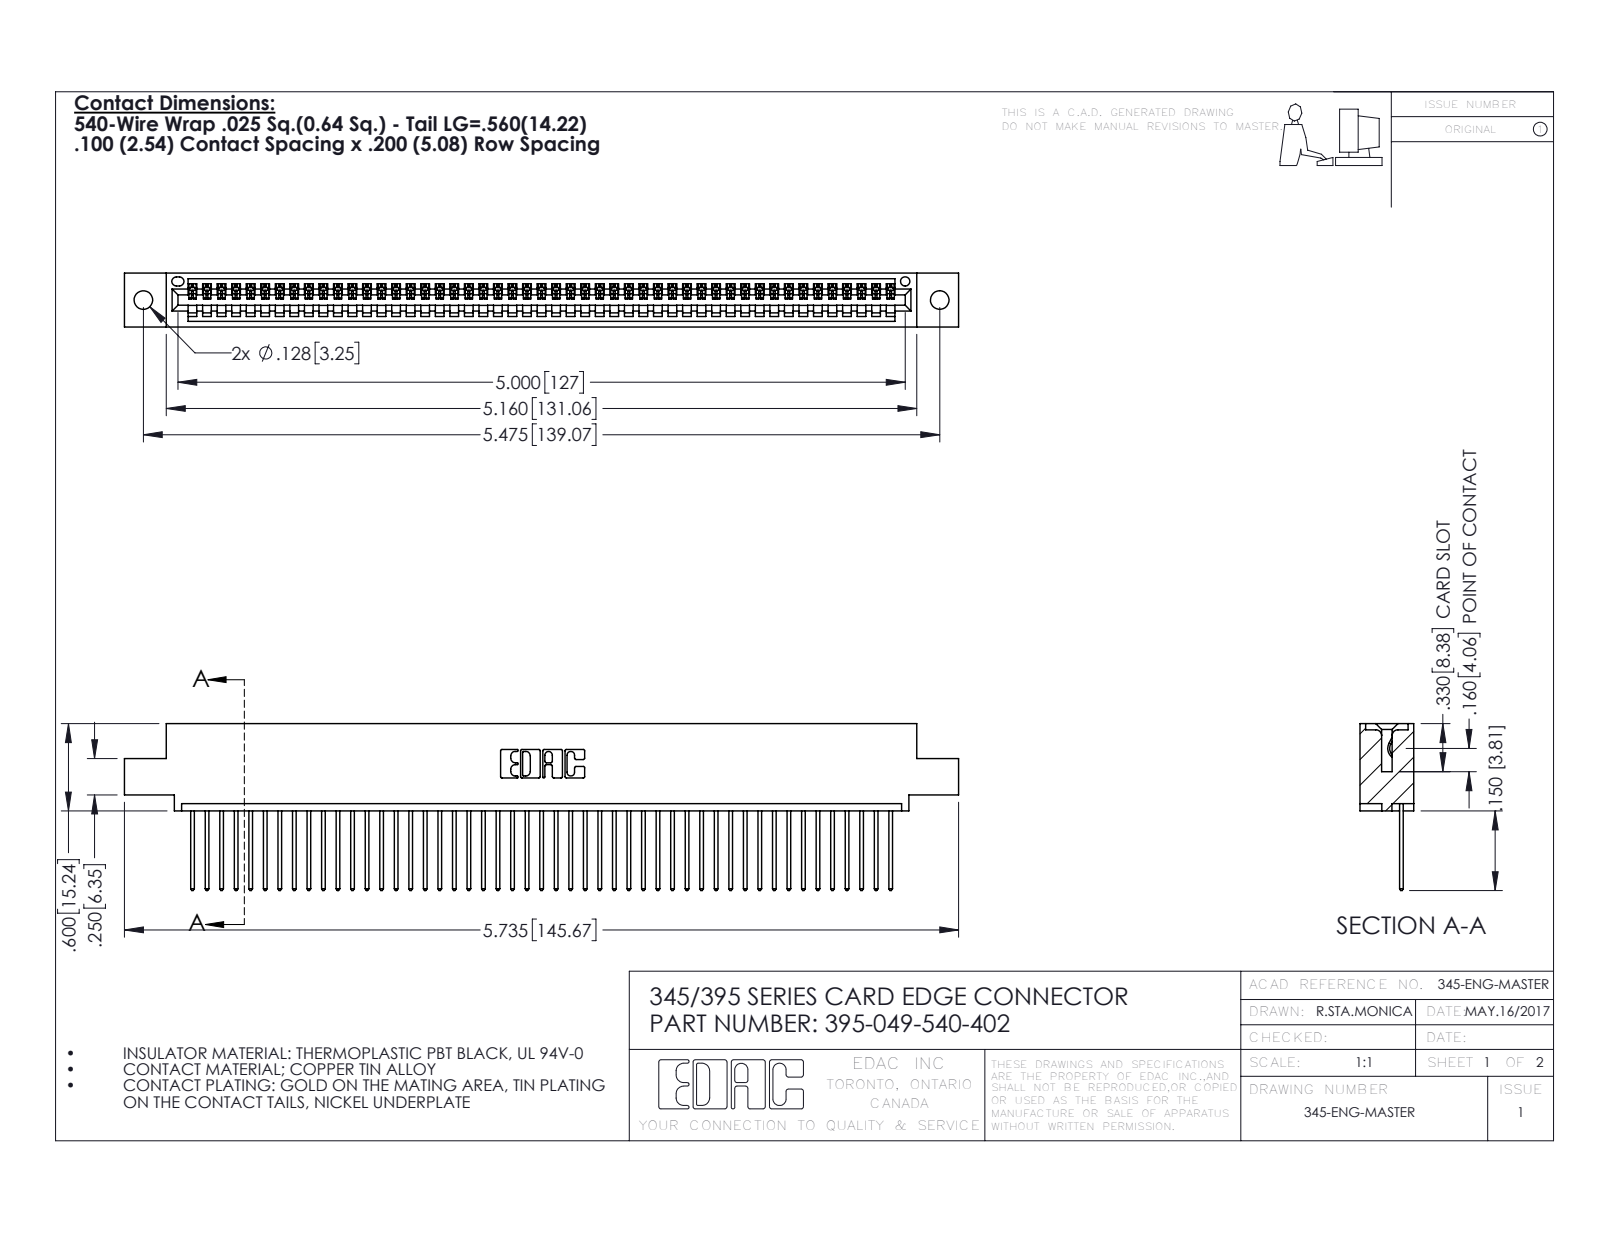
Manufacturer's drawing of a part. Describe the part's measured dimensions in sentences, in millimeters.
The part is named "395-049-540-402; 345-292-001_345-293-140; 345 Part_0.110 Offset - 0.128 Dia". Its 3-D file was written by "SolidWorks 2016 (CONFIG_CONTROL_DESIGN)". It is 50 solids with 2972 faces: 2044 planar, 928 cylindrical and 0 other. Overall it measures 145.7 by 29.1 by 9.4 millimeters. Its volume is 13 800 cubic millimeters and its surface area 18 790 square millimeters. Round holes: 2 of diameter 3.3, 1 of diameter 1.6. Partial cylindrical surfaces (rounded edges, fillets, slot ends): 98 of radius 0.2, 98 of radius 0.3, 22 of radius 0.3, 6 of radius 0.2, 6 of radius 0.8, 3 of radius 0.7, 2 of radius 0.8, 2 of radius 1. The main face-to-face distances are 7.6, 1.8, 9.4, 2.5, 6.9, 0.6, 5.1, 5.7, 3.8, 1.8. The hole center spacings are 6.9, 133.1, 139.1.
